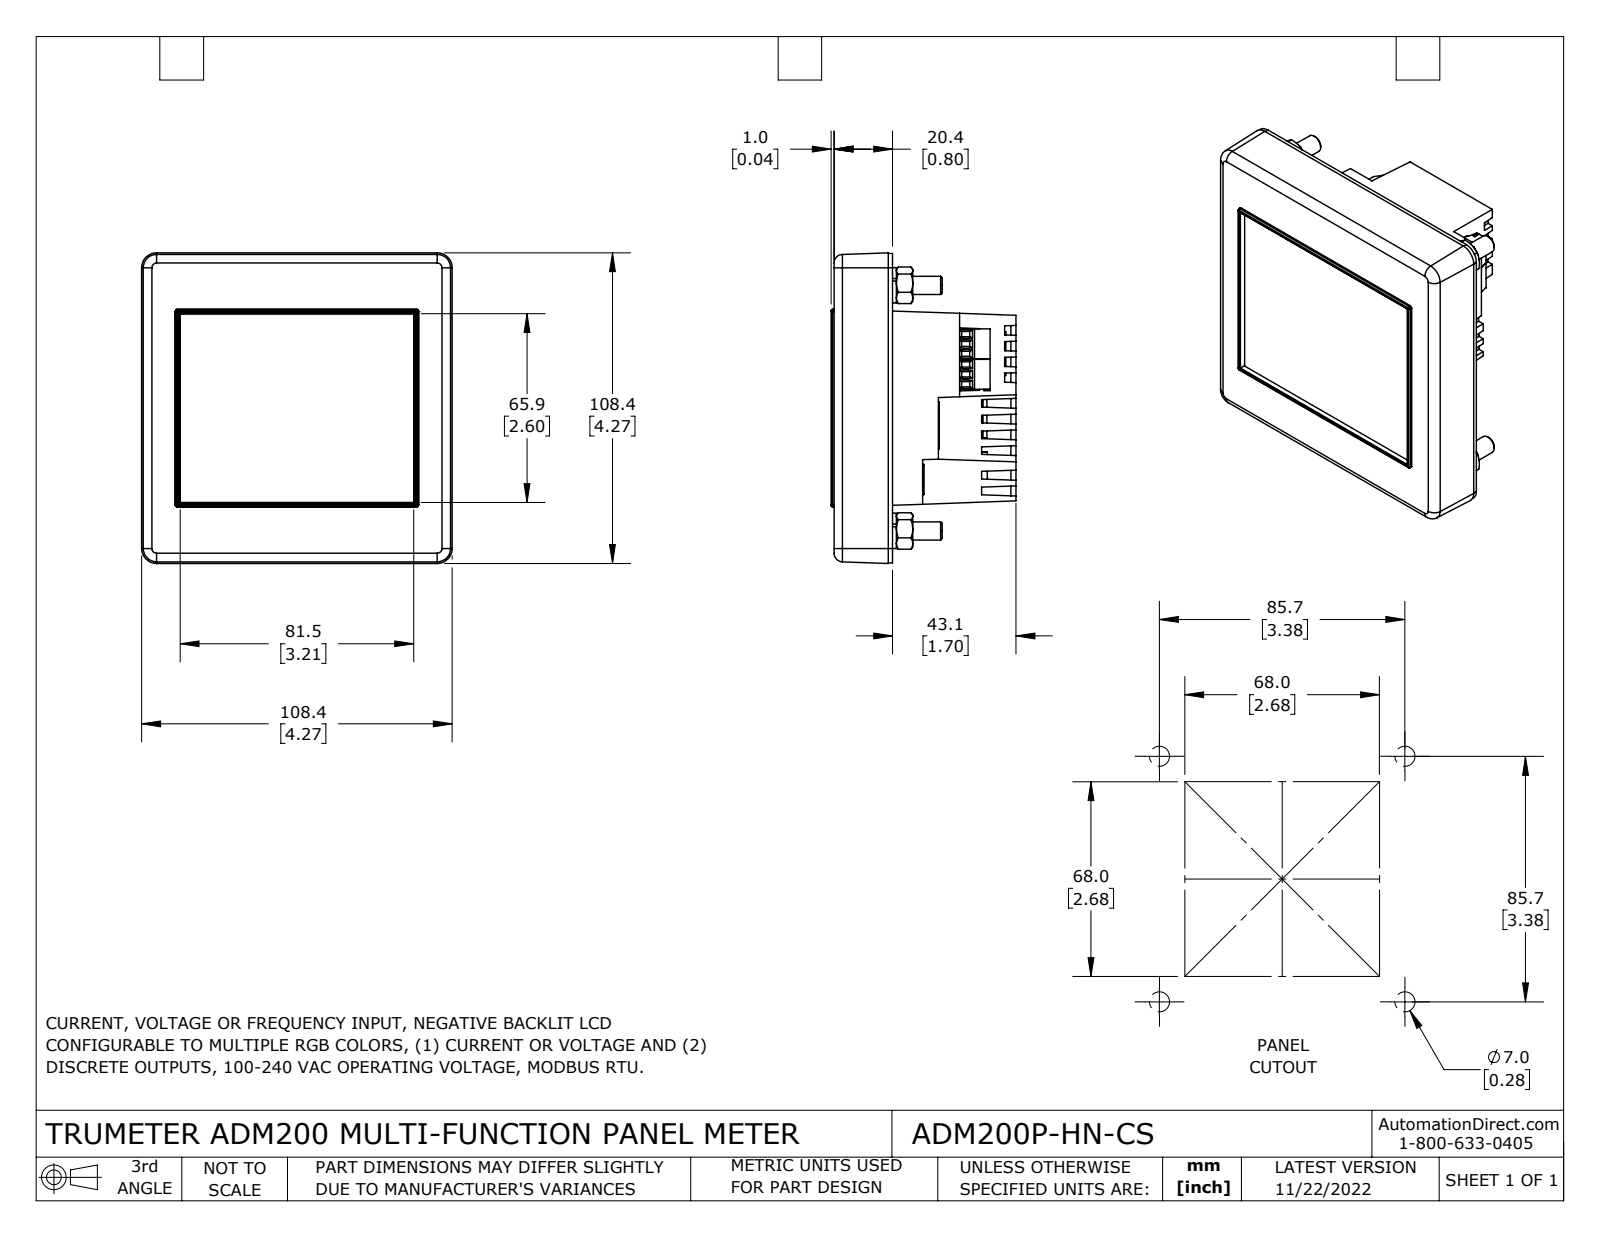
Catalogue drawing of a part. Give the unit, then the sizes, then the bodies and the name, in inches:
Units: inches
Overall size (bounding box): 4.269 × 4.269 × 2.541
Round holes (diameter × count): ⌀0.071 ×9, ⌀0.114 ×6, ⌀0.118 ×5, ⌀0.213 ×4, ⌀0.25 ×4, ⌀0.26 ×4, ⌀0.295 ×4, ⌀0.154 ×2
Round bosses / shafts (diameter × count): ⌀0.039 ×5, ⌀0.487 ×4, ⌀0.438 ×4, ⌀0.024 ×4, ⌀0.079 ×2
Partial cylindrical surfaces — rounded edges, fillets, slot ends (radius × count): R0.006 ×32, R0.02 ×30, R0.039 ×7, R0.016 ×4, R0.03 ×4, R0.118 ×4, R0.197 ×4, R0.004 ×2
Main face-to-face distances: 0.031, 0.635, 0.11, 0.073, 0.059, 0.079, 0.694, 3.395, 3.468, 0.047
Hole centre spacings: 0.709, 3.228, 0.136, 0.293, 0.986, 1.417, 2.126, 2.399
Volume: 7.808 in³ · Surface area: 190.8 in²
Bodies: 23 solids, 2059 faces (1384 planar, 290 cylindrical, 385 other)
Part name (STEP PRODUCT): ADM200P-HN-CS
STEP written by: SolidWorks 2021 (CONFIG_CONTROL_DESIGN)
